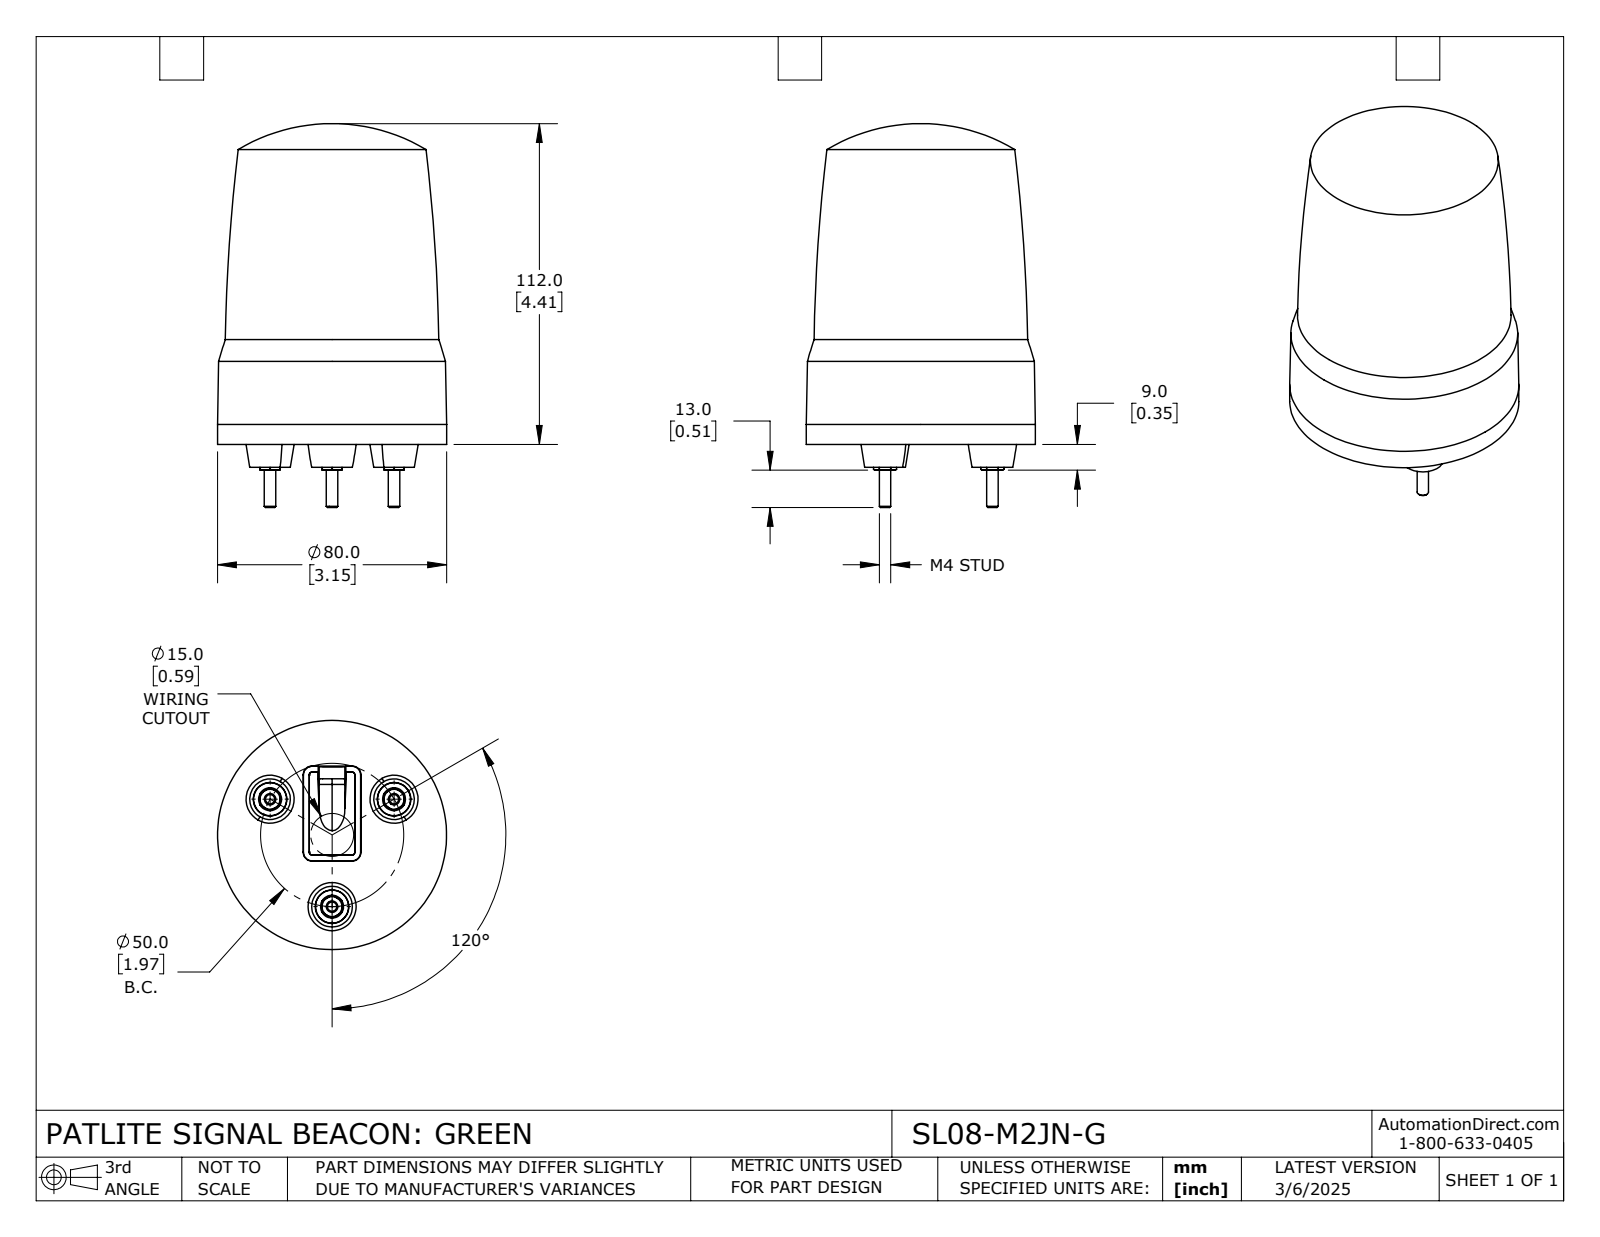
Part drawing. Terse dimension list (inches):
name: SL08-M2JN-G
written by: SolidWorks 2024 (CONFIG_CONTROL_DESIGN)
unit: in
bodies: 1 solid, 138 faces (47 planar, 14 cylindrical, 77 other)
size: 5.276 × 3.15 × 3.15
volume: 28.27 in³; area: 54.88 in²
bosses: 3× ⌀0.315, 3× ⌀0.157, 1× ⌀3.15
face distances: 0.033, 0.096, 0.063, 0.209, 0.242, 0.305, 0.106, 0.315, 0.348, 0.411
